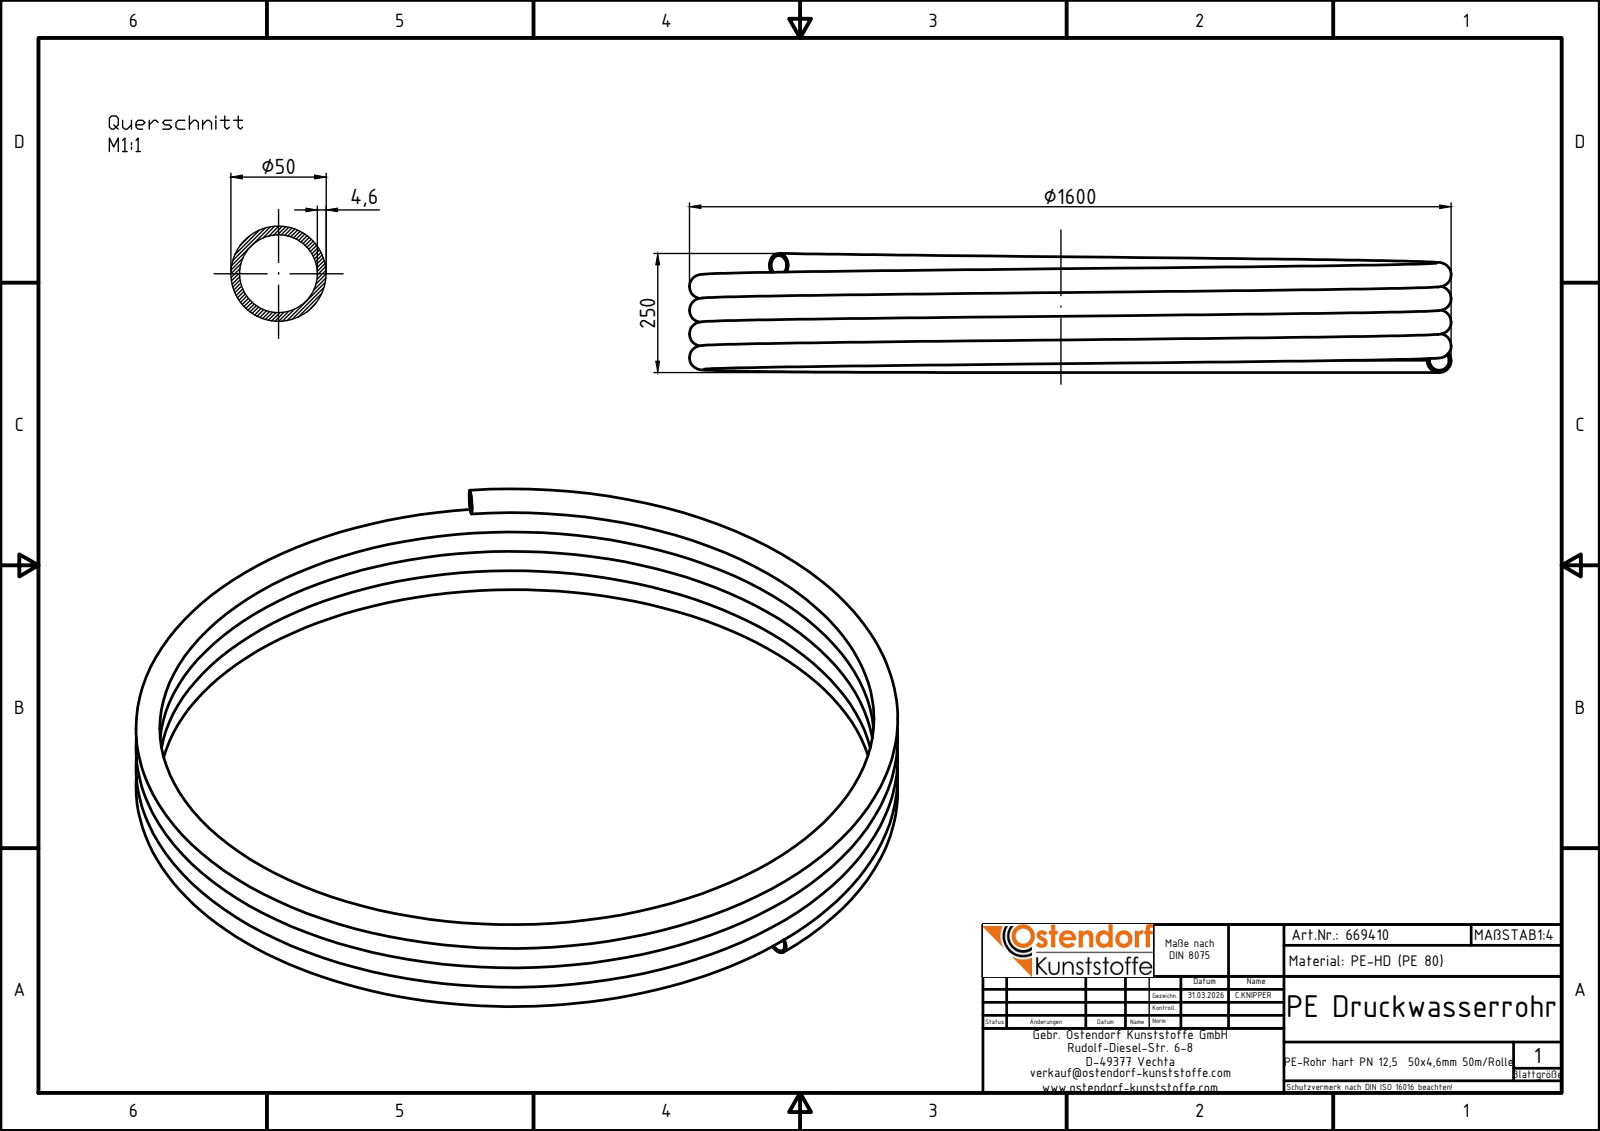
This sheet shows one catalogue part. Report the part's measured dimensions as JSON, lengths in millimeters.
{"part_name": "669410z", "step_written_by": "Autodesk Inventor 2024 (AUTOMOTIVE_DESIGN)", "units": "millimeters", "bodies": {"solids": 1, "faces": 7, "planar": 3, "cylindrical": 0, "other": 4}, "overall_size": [1600, 1600, 250.2], "volume_mm3": 13670000, "surface_area_mm2": 5825000}
